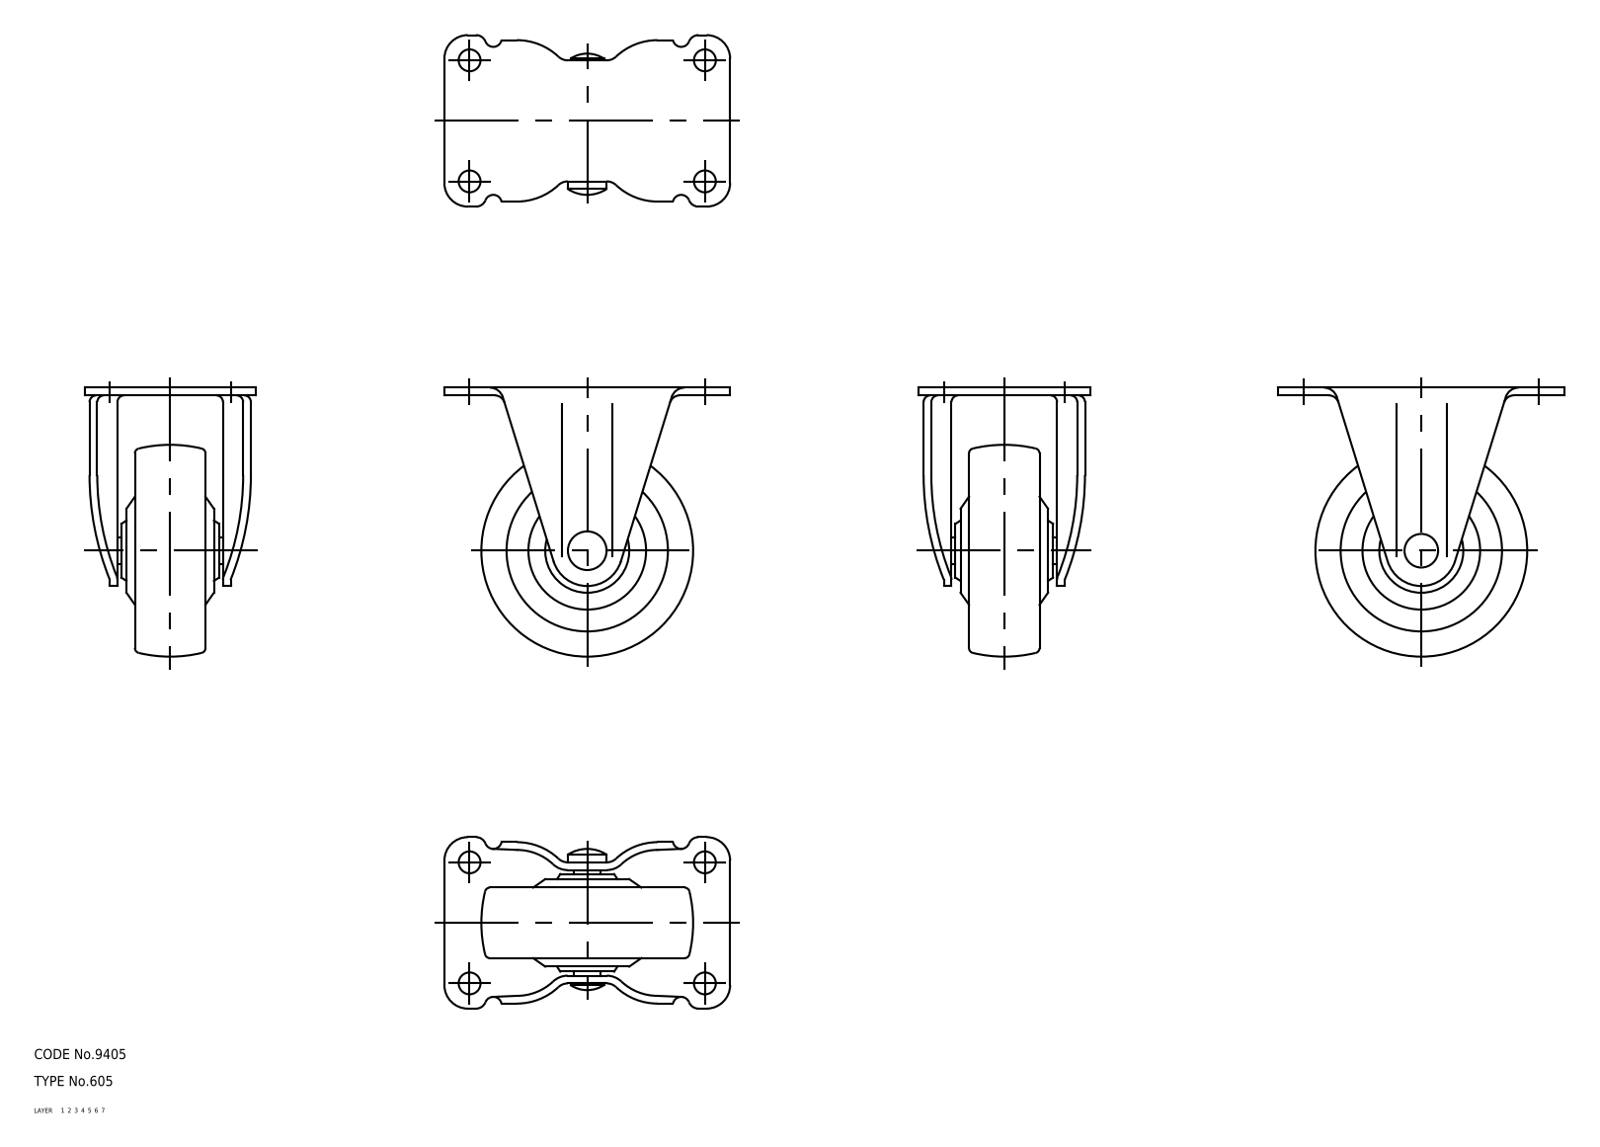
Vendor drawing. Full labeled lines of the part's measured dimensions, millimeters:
Part name (STEP PRODUCT): wheel; axle; No_605_15077_36
STEP written by: CADfix (AUTOMOTIVE_DESIGN)
Units: millimetres
Bodies: 3 solids, 136 faces (0 planar, 0 cylindrical, 136 other)
Overall size (bounding box): 85 × 80 × 51
Volume: 83 373 mm³ · Surface area: 28 227 mm²
